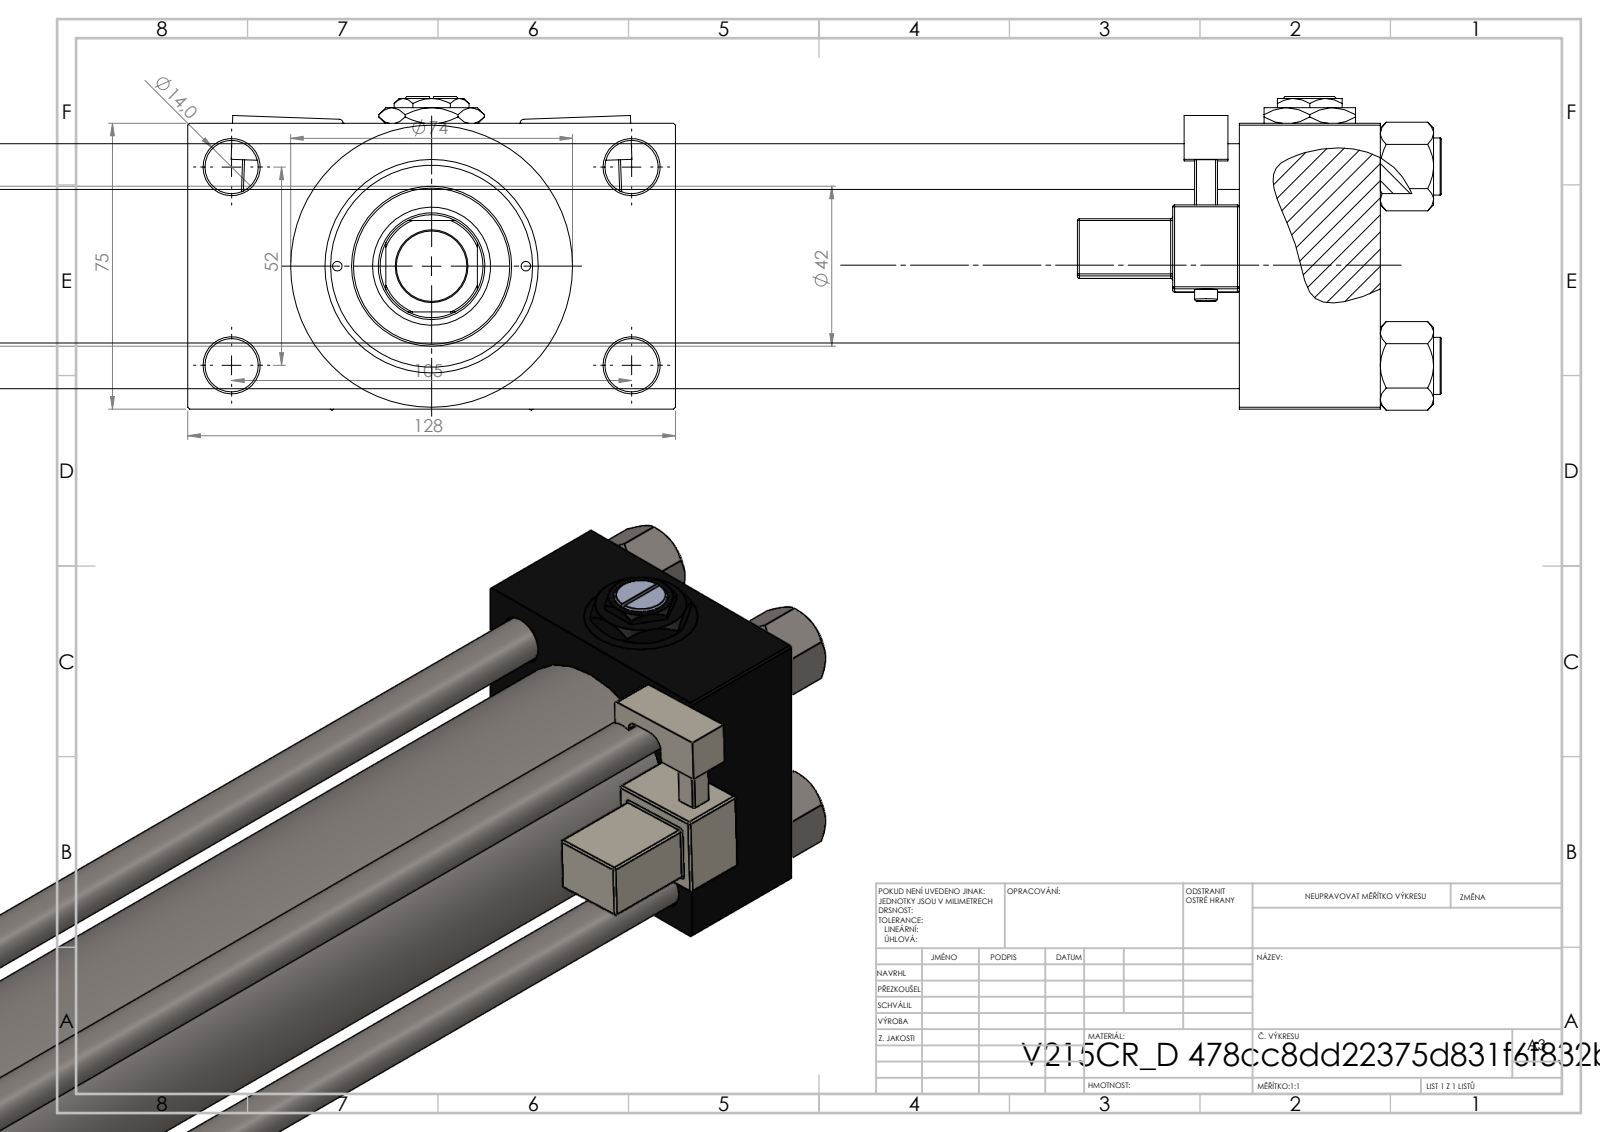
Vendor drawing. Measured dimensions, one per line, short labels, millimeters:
name: Zatka_pro_OIL_PORT; V215CR_MSU; V215CR_D_TYCINKA; V215_VC_A (+3 more)
written by: SolidWorks 2019 (CONFIG_CONTROL_DESIGN)
unit: mm
bodies: 15 solids, 1366 faces (605 planar, 163 cylindrical, 598 other)
size: 575 × 128 × 82.27
volume: 1 438 000 mm³; area: 404 319 mm²
holes: 4× ⌀12, 4× ⌀14, 4× ⌀20.96, 4× ⌀30, 3× ⌀7, 2× ⌀2.5, 1× ⌀18.5, 1× ⌀28, 1× ⌀31, 1× ⌀41, 1× ⌀50, 1× ⌀53
bosses: 4× ⌀15, 2× ⌀6, 1× ⌀74, 1× ⌀56, 1× ⌀42
rounds: 48× R0.5, 2× R1, 2× R2.5, 2× R4, 1× R13.5
face distances: 75, 438, 37, 475, 26.5, 101.5, 518, 481, 43, 16
hole spacings: 26.19, 26.35, 36.98, 38.03, 52.3, 57.22, 58.43, 58.59
